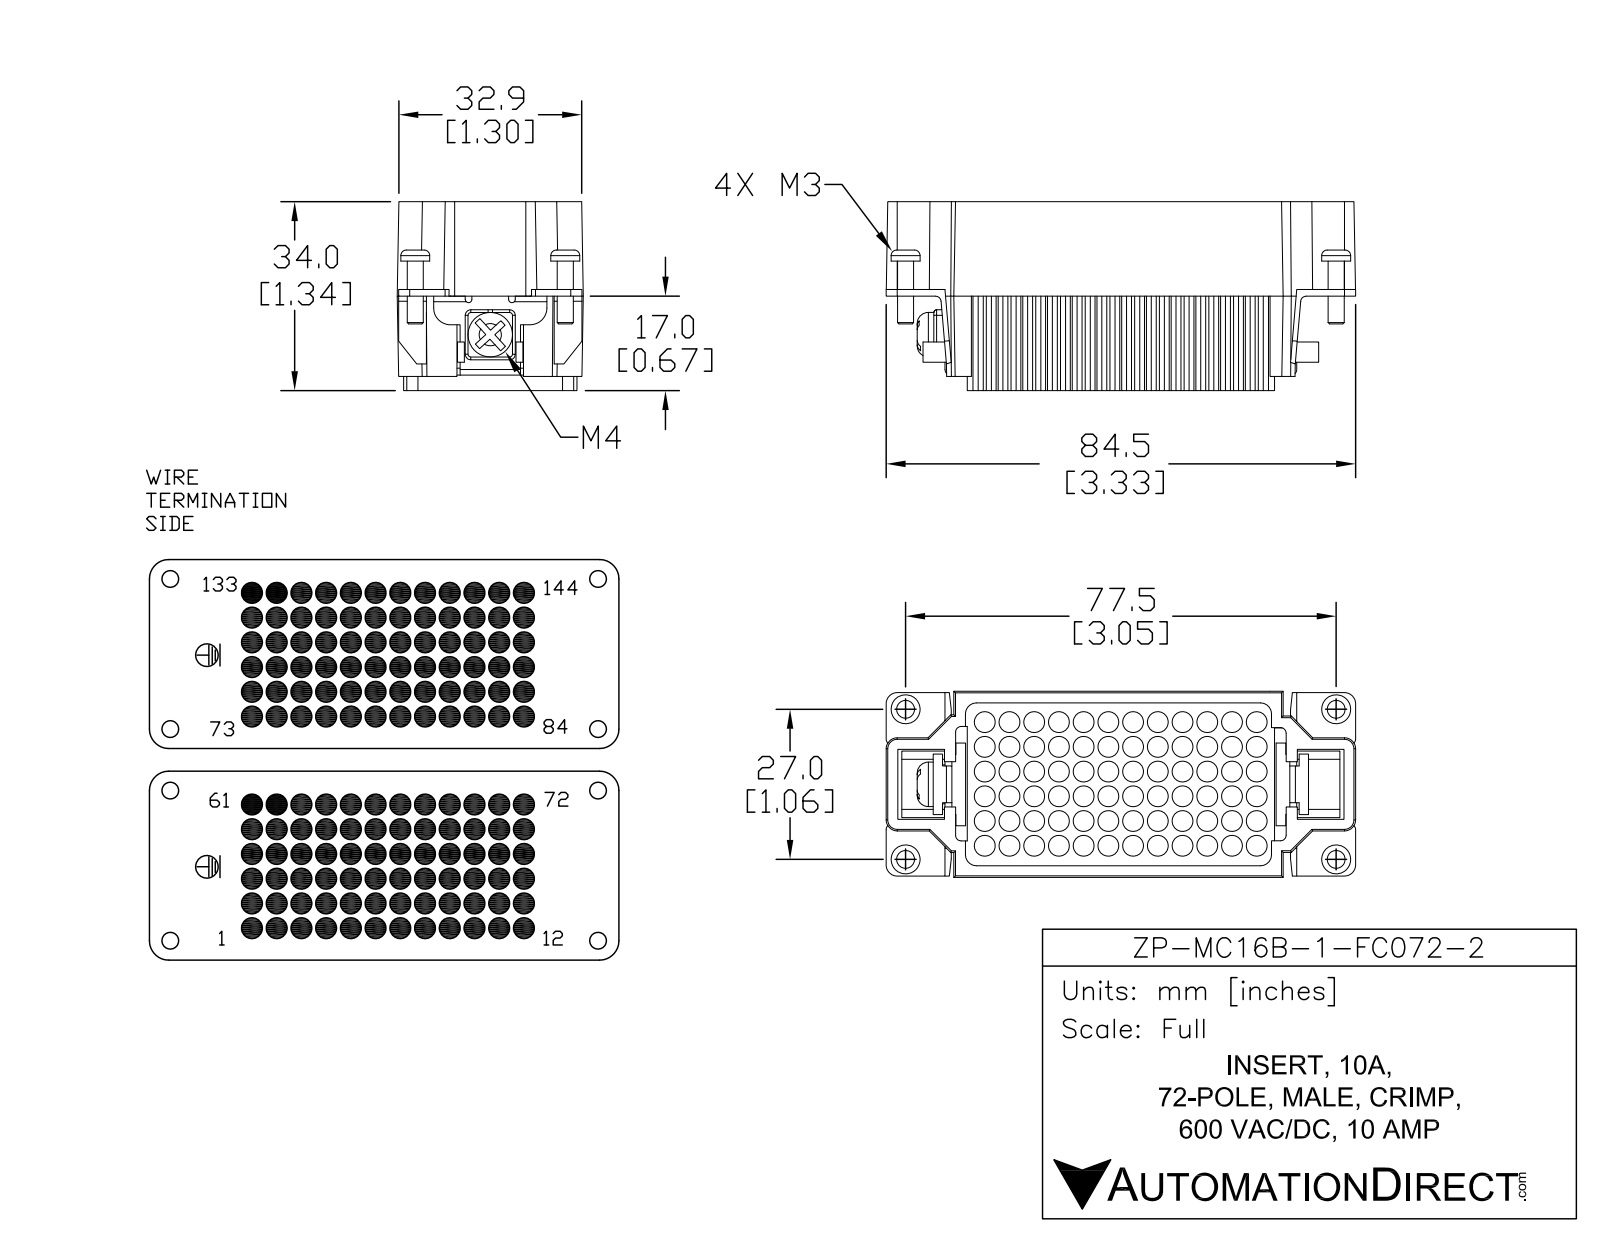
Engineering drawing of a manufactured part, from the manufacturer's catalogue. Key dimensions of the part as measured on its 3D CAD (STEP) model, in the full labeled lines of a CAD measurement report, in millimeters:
Part name (STEP PRODUCT): ZP-MC16B-1-FC072-2
STEP written by: SolidWorks 2021 (CONFIG_CONTROL_DESIGN)
Units: millimetres
Bodies: 1 solid, 2630 faces (884 planar, 805 cylindrical, 941 other)
Overall size (bounding box): 84.3 × 33.7 × 33.6
Volume: 52 110 mm³ · Surface area: 24 170 mm²
Round holes (diameter × count): ⌀3.6 ×70, ⌀3.9 ×1
Round bosses / shafts (diameter × count): ⌀5.4 ×4, ⌀3 ×4, ⌀2.3 ×4, ⌀7 ×1, ⌀5 ×1, ⌀4 ×1, ⌀3.6 ×1
Partial cylindrical surfaces — rounded edges, fillets, slot ends (radius × count): R0.2 ×160, R0.5 ×88, R0.3 ×70, R1.2 ×52, R1 ×24, R1.5 ×12, R0.8 ×8, R0.8 ×4
Main face-to-face distances: 1.2, 14.1, 17.7, 3, 0.9, 2.4, 4.3, 2, 13.2, 10.2
Hole centre spacings: 4.5, 10.1, 6.4, 9, 14.2, 18.5, 23, 13.5
